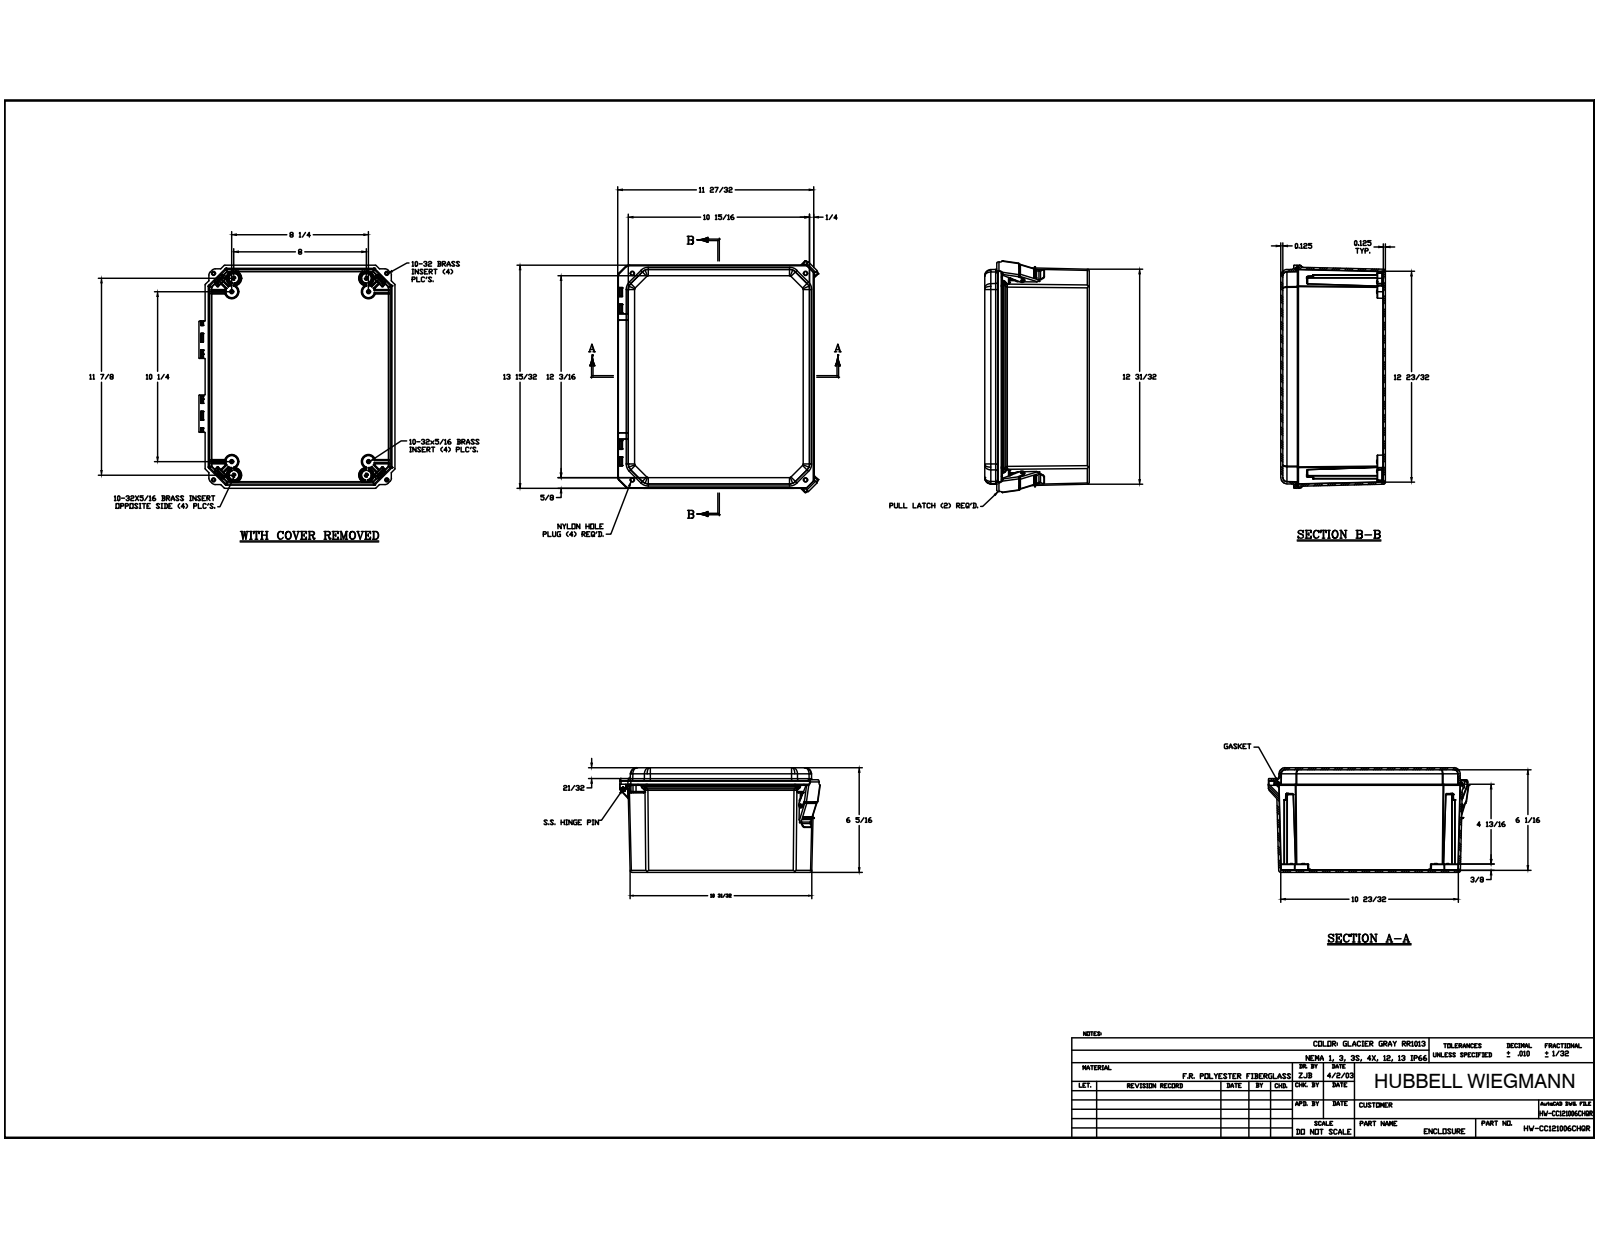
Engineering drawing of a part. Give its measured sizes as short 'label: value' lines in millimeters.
name: DS121006BOX; DSCC121006CVR; GA1210; WP1210HLU (+6 more)
written by: Autodesk Inventor 2014 (AUTOMOTIVE_DESIGN)
unit: mm
bodies: 29 solids, 2223 faces (661 planar, 878 cylindrical, 684 other)
size: 358.6 × 309 × 160.32
volume: 1 380 000 mm³; area: 817 564 mm²
holes: 12× ⌀3.96, 8× ⌀3.86, 6× ⌀3.43, 4× ⌀3.81, 4× ⌀5.56, 4× ⌀6.4, 4× ⌀7.92, 2× ⌀3.43, 2× ⌀3.48, 2× ⌀9.52
bosses: 12× ⌀6.25, 4× ⌀22.1, 4× ⌀5.3, 2× ⌀7.62, 2× ⌀3.43
rounds: 188× R0.25, 94× R0.13, 59× R0.51, 58× R0.76, 29× R3.17, 26× R2.29, 24× R0.76, 24× R1.52
face distances: 3.17, 157.15, 160.32, 153.98, 3.53, 3.55, 3.56, 140.49, 16.66, 25.4
hole spacings: 32.02, 234.48, 289.71, 6.35, 20.92, 39.6, 281.04, 289.7
